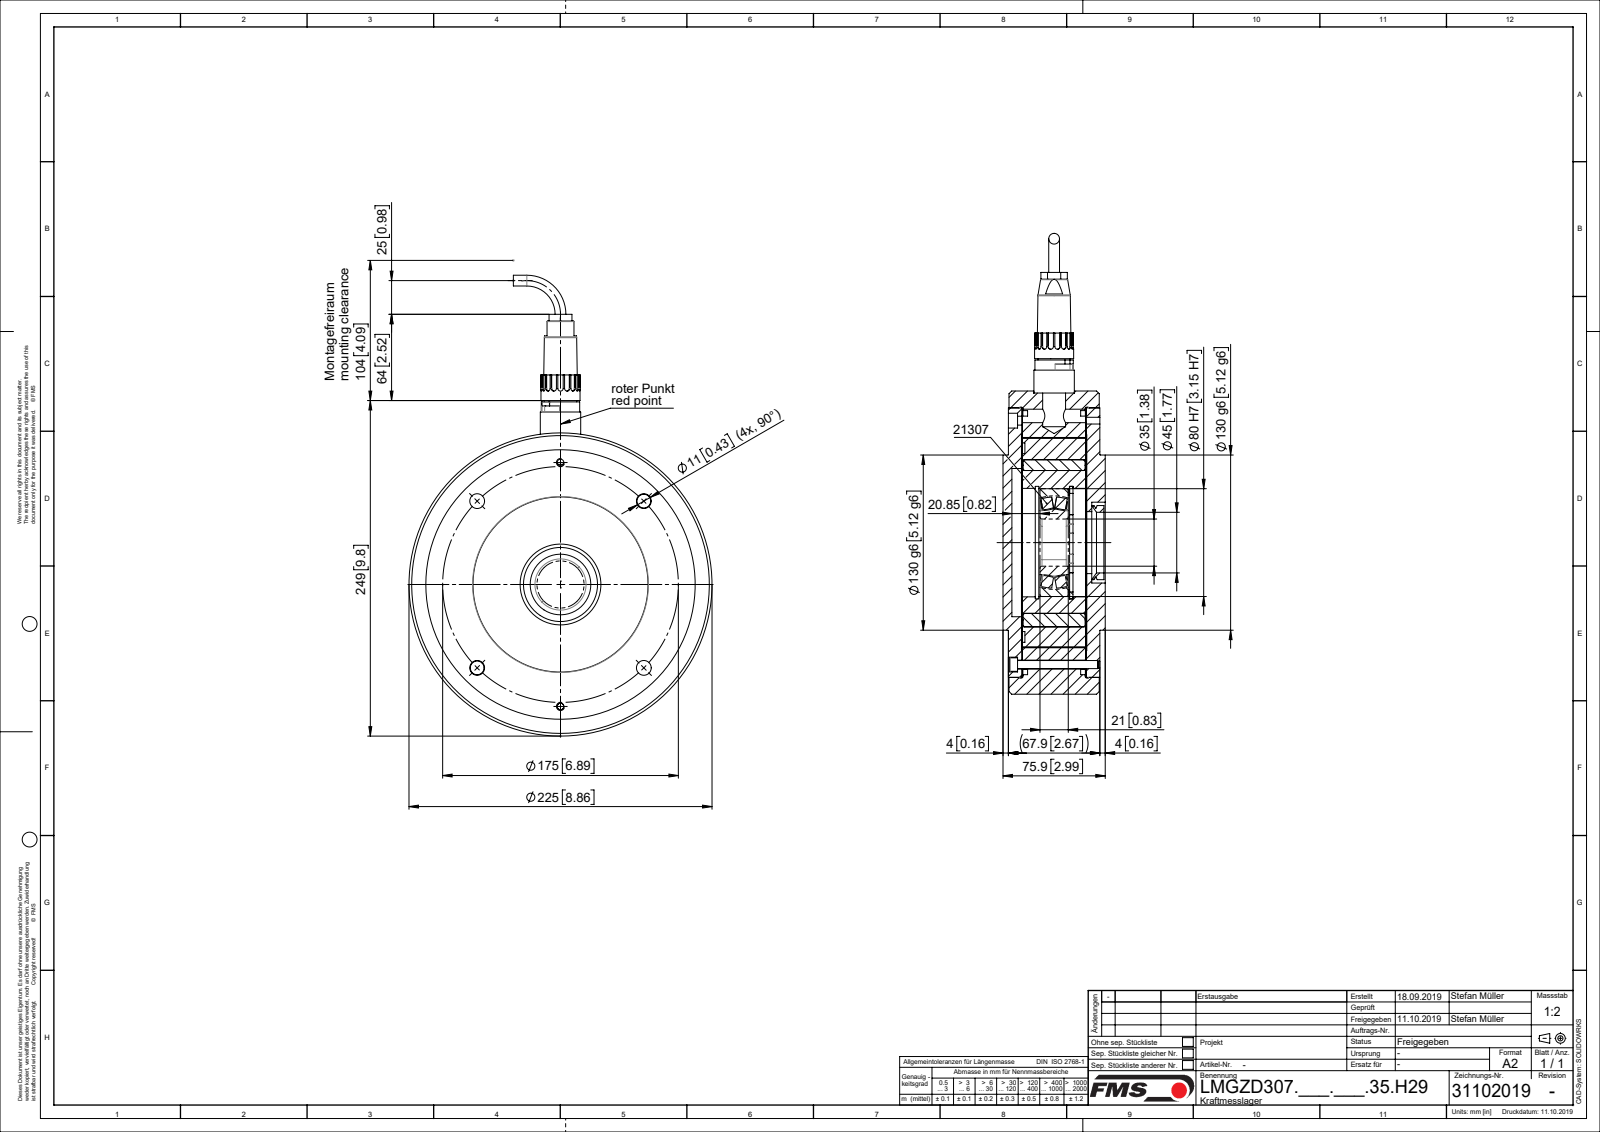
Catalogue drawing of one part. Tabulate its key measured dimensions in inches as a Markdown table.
| quantity | value |
| --- | --- |
| part name | 49531_01; 48071_01; 49651-04_stp_01; Flanschstecker_Kunstst_7Pol_01 (+8 more) |
| STEP written by | SolidWorks 2018 (CONFIG_CONTROL_DESIGN) |
| units | inches |
| bodies | 49 solids, 814 faces (225 planar, 334 cylindrical, 255 other) |
| overall size | 13.465 × 8.858 × 2.988 |
| volume | 148.3 in³ |
| surface area | 705.9 in² |
| round holes (diameter × count) | 0.433 × 6, 0.098 × 4, 0.118 × 2, 0.134 × 2, 0.142 × 2, 0.197 × 2, 0.26 × 2, 0.394 × 2, 0.402 × 2, 0.315 × 1, 0.413 × 1, 0.551 × 1 |
| round bosses / shafts (diameter × count) | 0.085 × 7, 0.217 × 2, 0.118 × 2, 8.858 × 1, 7.835 × 1, 7.402 × 1, 5.512 × 1, 5.197 × 1 |
| partial cylindrical surfaces (radius × count) | 0.079 × 17, 0.004 × 4, 0.433 × 4, 0.118 × 2, 0.193 × 2, 1.309 × 1, 3.11 × 1, 3.228 × 1 |
| main face-to-face distances | 1.86, 0.402, 0.411, 2.262, 2.272, 1.89, 0.03, 0.02, 1.88, 0.382 |
| hole center spacings | 0.64, 0.885, 0.906, 2.442, 2.684, 3.445, 4.872, 5.293 |
